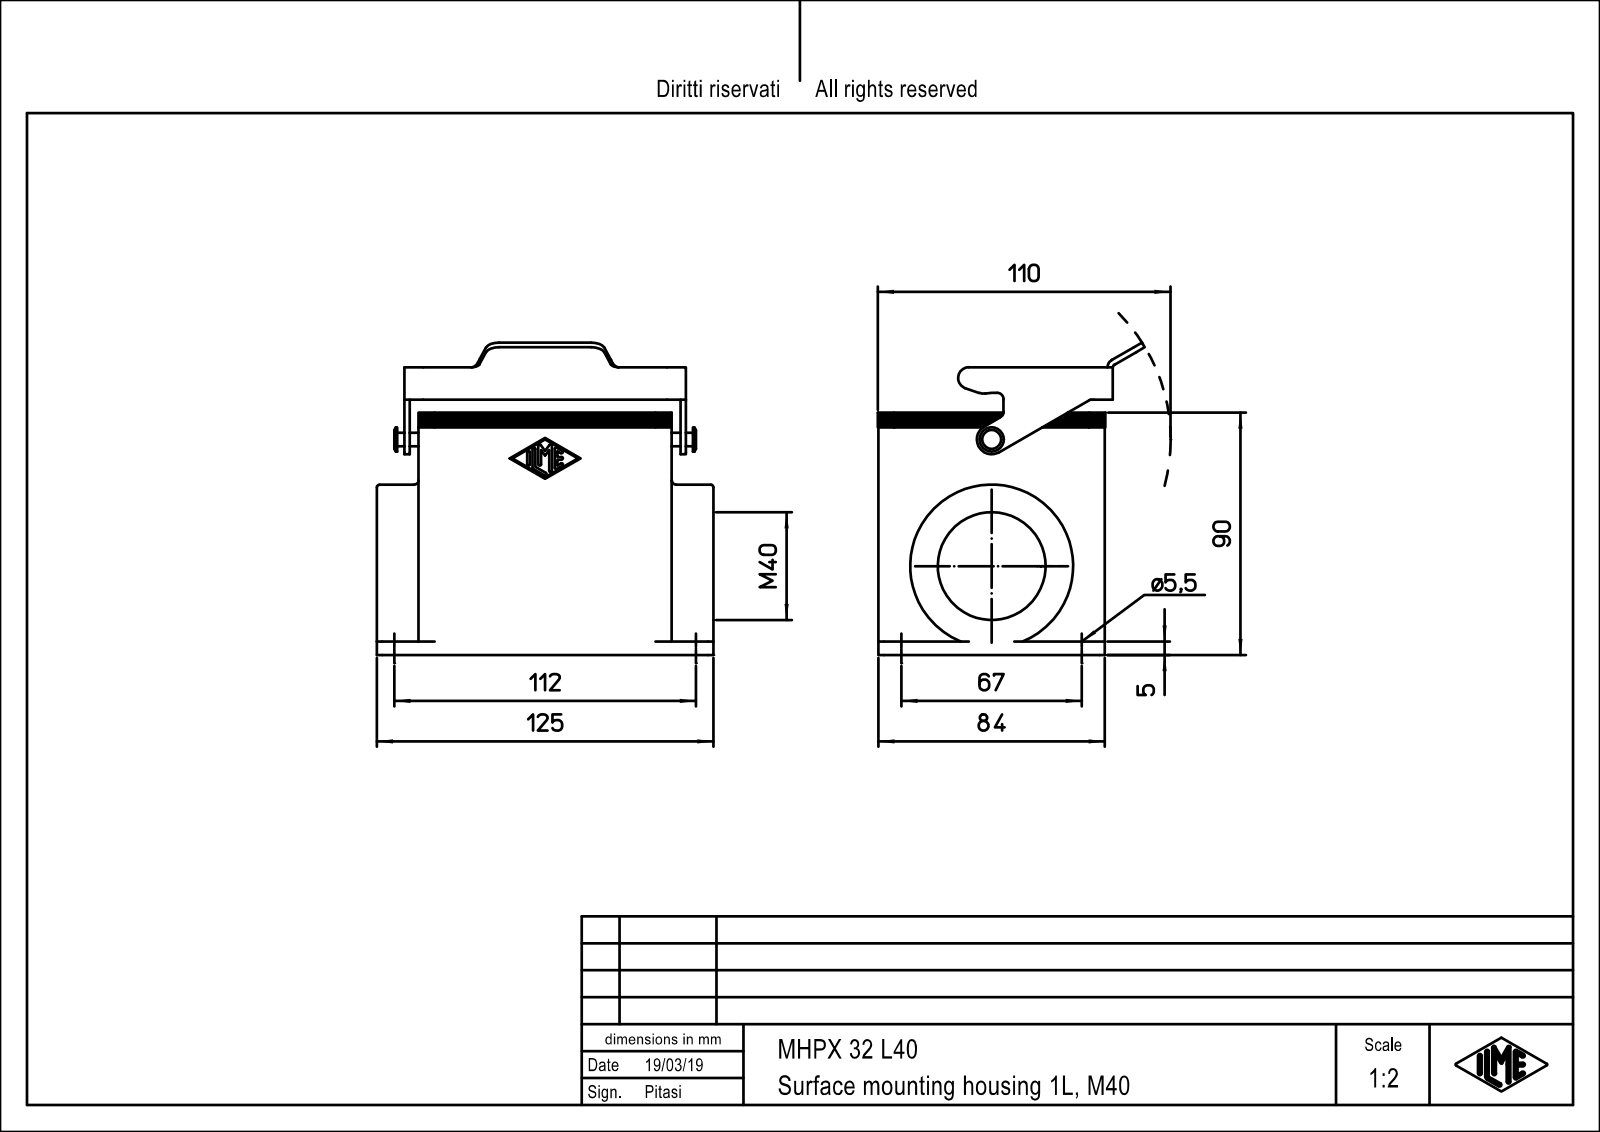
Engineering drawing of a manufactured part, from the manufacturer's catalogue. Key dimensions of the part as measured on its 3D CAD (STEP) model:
Part name (STEP PRODUCT): CHPX_32_L; MHPX_32_L40; MHPX_32_L40.stp
STEP written by: PTC Creo Elements/Direct Modeling 19.0E 27-Jun-2016 (C) Parametric Technology GmbH (AUTOMOTIVE_DESIGN)
Units: millimetres
Bodies: 1 solid, 202 faces (90 planar, 102 cylindrical, 10 other)
Overall size (bounding box): 125 × 115.96 × 99.11
Volume: 250 422 mm³ · Surface area: 100 198 mm²
Round holes (diameter × count): ⌀3 ×8, ⌀5.5 ×4, ⌀30 ×1, ⌀40 ×1
Round bosses / shafts (diameter × count): ⌀60.5 ×1, ⌀9 ×1, ⌀5 ×1
Partial cylindrical surfaces — rounded edges, fillets, slot ends (radius × count): R1.5 ×9, R2 ×8, R6 ×8, R3 ×7, R5 ×5, R2.4 ×2, R7 ×2, R1 ×1
Main face-to-face distances: 3, 81, 4, 84, 78, 11.5, 82.5, 2, 71, 1
Hole centre spacings: 17.37, 27, 33.74, 36, 41.73, 67.25, 77.5, 82.07
